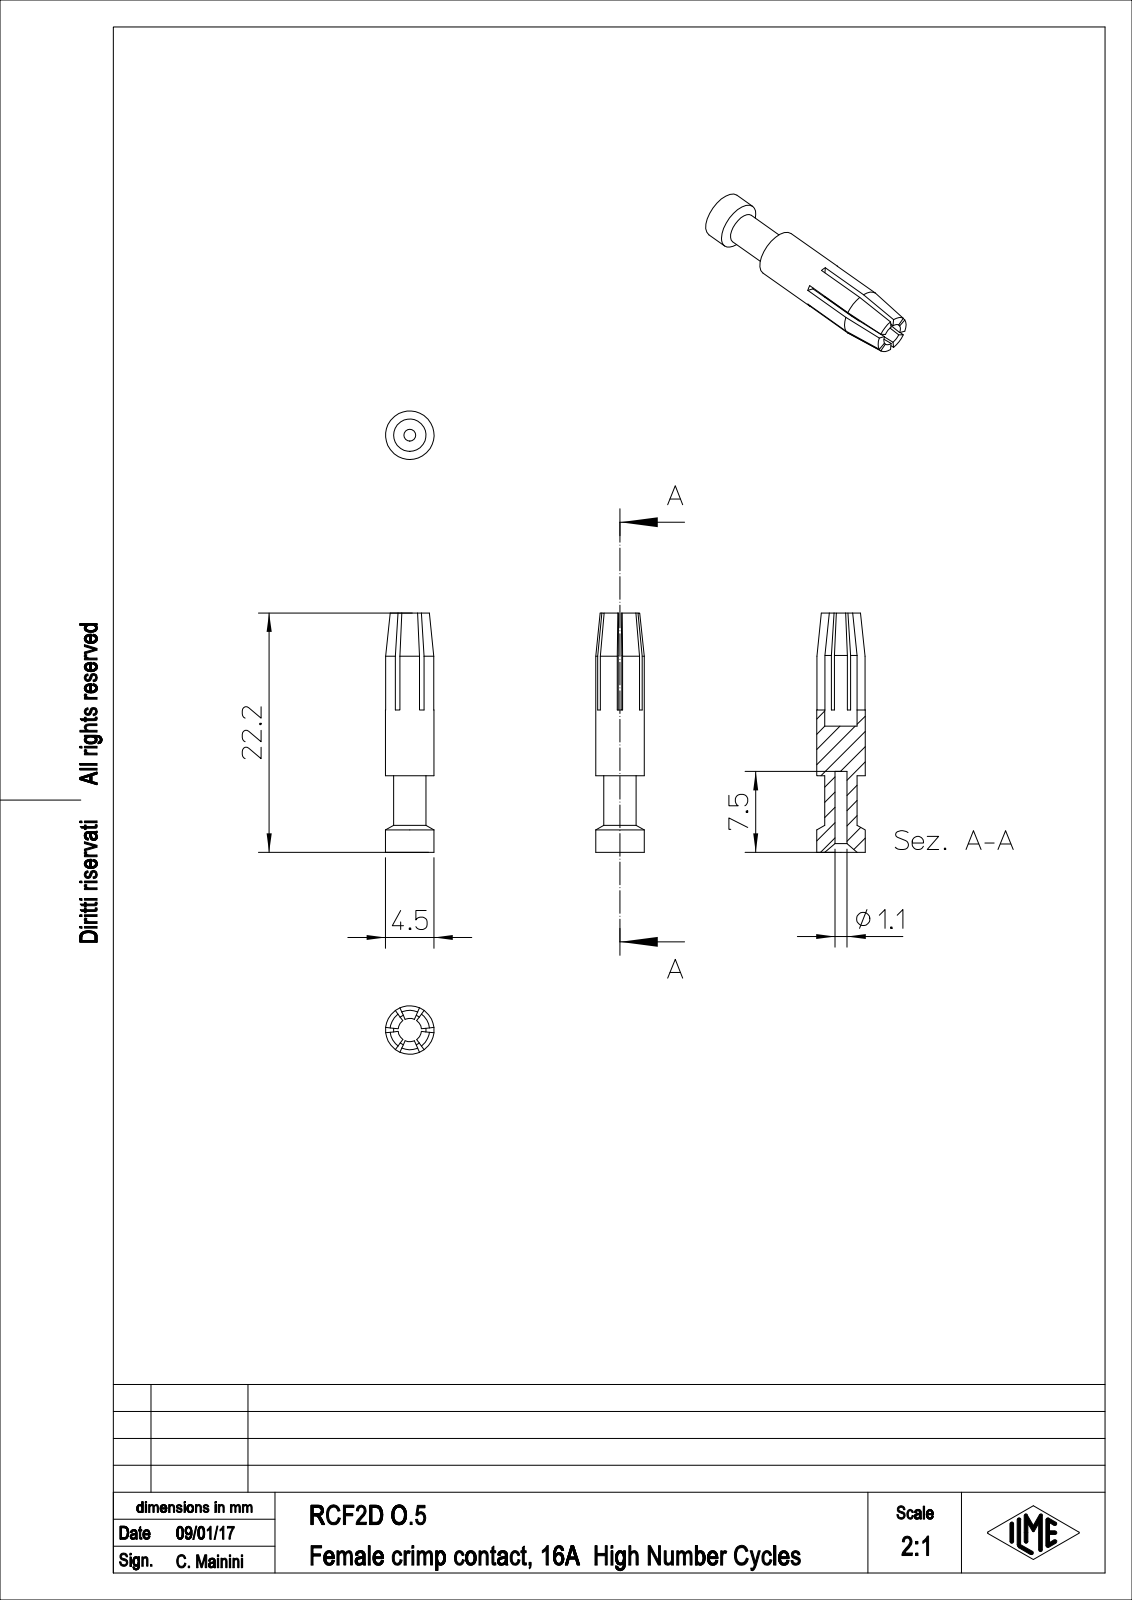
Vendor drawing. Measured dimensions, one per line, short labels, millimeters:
name: RCF2D_0.5
written by: PTC Creo Elements/Direct Modeling 19.0E 27-Jun-2016 (C) Parametric Technology GmbH (AUTOMOTIVE_DESIGN)
unit: mm
bodies: 1 solid, 54 faces (28 planar, 10 cylindrical, 16 other)
size: 22.2 × 4.5 × 4.5
volume: 207 mm³; area: 487 mm²
holes: 1× ⌀1.1, 1× ⌀3
bosses: 1× ⌀4.5
face distances: 7.1, 4.6, 11.7, 10.5, 15.1, 22.2, 9, 1.5, 6.1, 13.2
